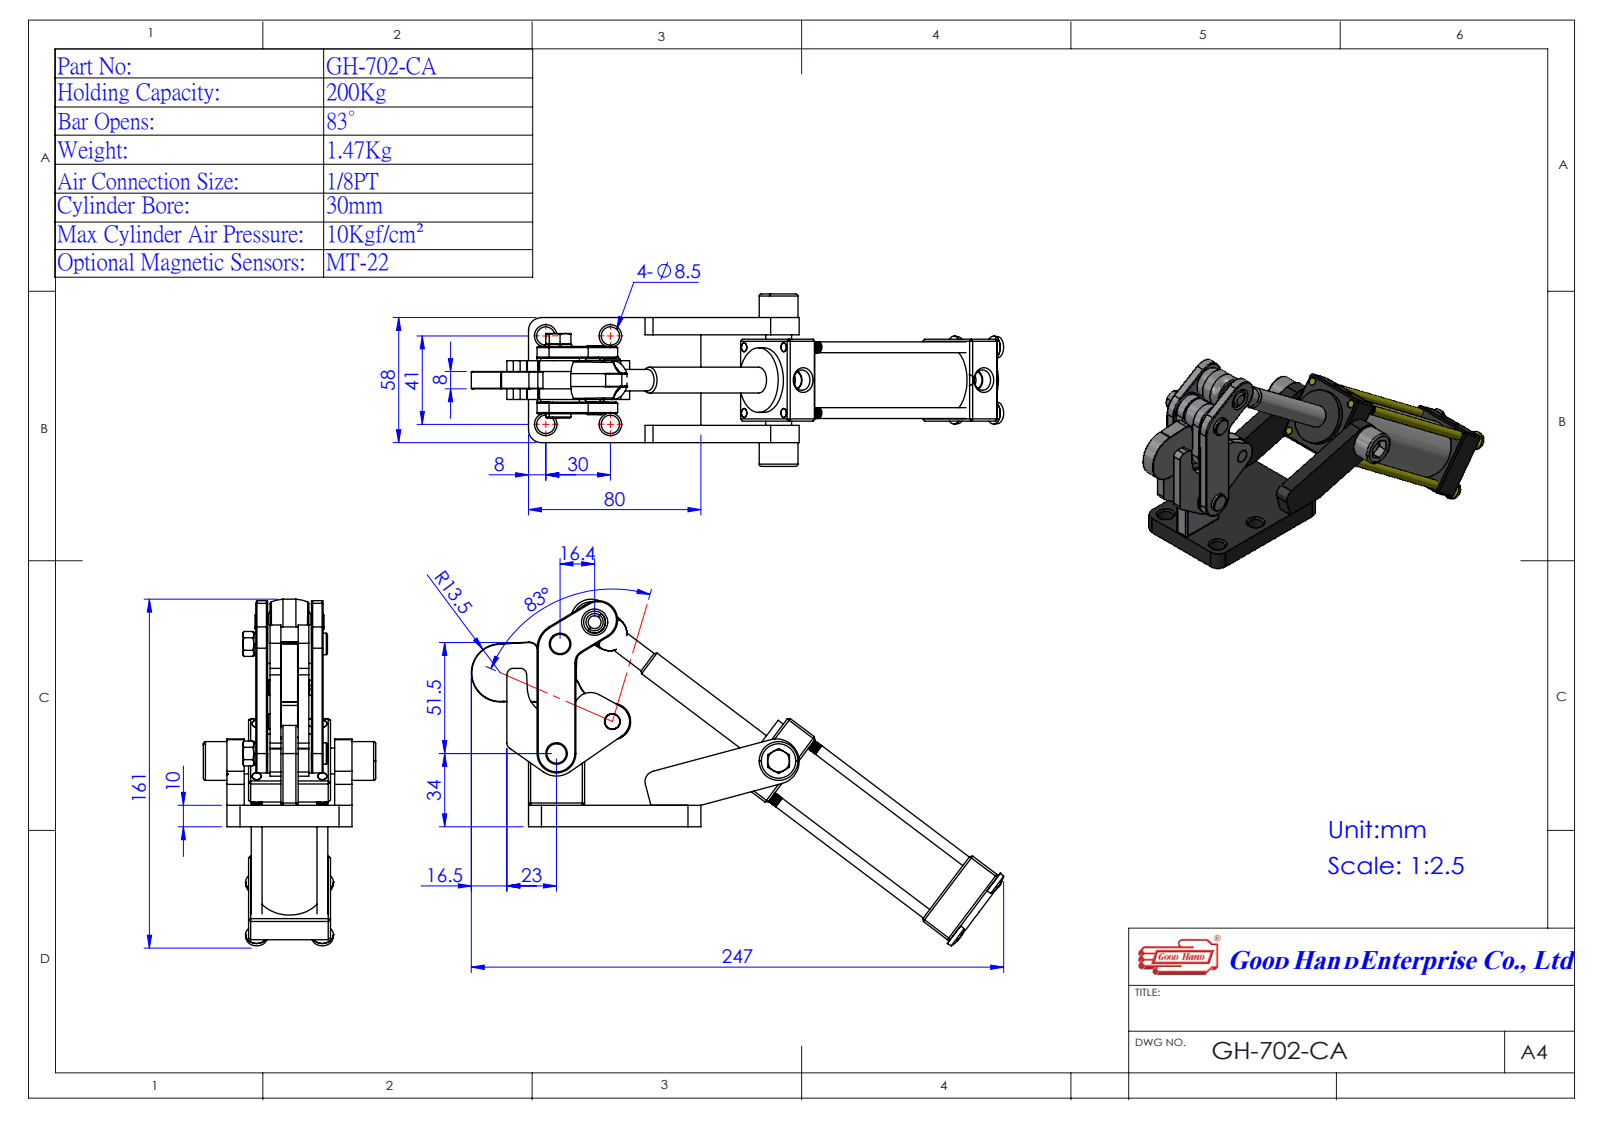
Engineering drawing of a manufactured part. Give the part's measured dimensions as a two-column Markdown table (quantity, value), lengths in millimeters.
| quantity | value |
| --- | --- |
| part name | Group6^GH-702-CA(簡化); 3700108-1^GH-702-CA(簡化); Group3^GH-702-CA(簡化); 702CA氣缸-1^GH-702-CA(簡化) (+4 more) |
| STEP written by | SolidWorks 2016 (AUTOMOTIVE_DESIGN) |
| units | millimeters |
| bodies | 7 solids, 902 faces (398 planar, 263 cylindrical, 241 other) |
| overall size | 247.03 × 160.83 × 80 |
| volume | 225 378 mm³ |
| surface area | 99 276 mm² |
| round holes (diameter × count) | 4.2 × 8, 6 × 6, 8.5 × 4, 8.43 × 2, 12 × 1, 14 × 1, 30 × 1 |
| round bosses / shafts (diameter × count) | 10.3 × 4, 10 × 4, 5 × 4, 30 × 3, 18 × 3, 6.97 × 3, 32 × 1, 27 × 1 |
| partial cylindrical surfaces (radius × count) | 6 × 5, 3 × 3, 8 × 3, 8.5 × 2, 8.75 × 2, 9.5 × 2, 10.5 × 2, 3.6 × 1 |
| main face-to-face distances | 10, 8, 25, 5, 13, 38, 5.4, 20, 33, 18 |
| hole center spacings | 30.5, 21.56, 21.57, 21.58, 43.14, 30, 30.49, 30.51 |
